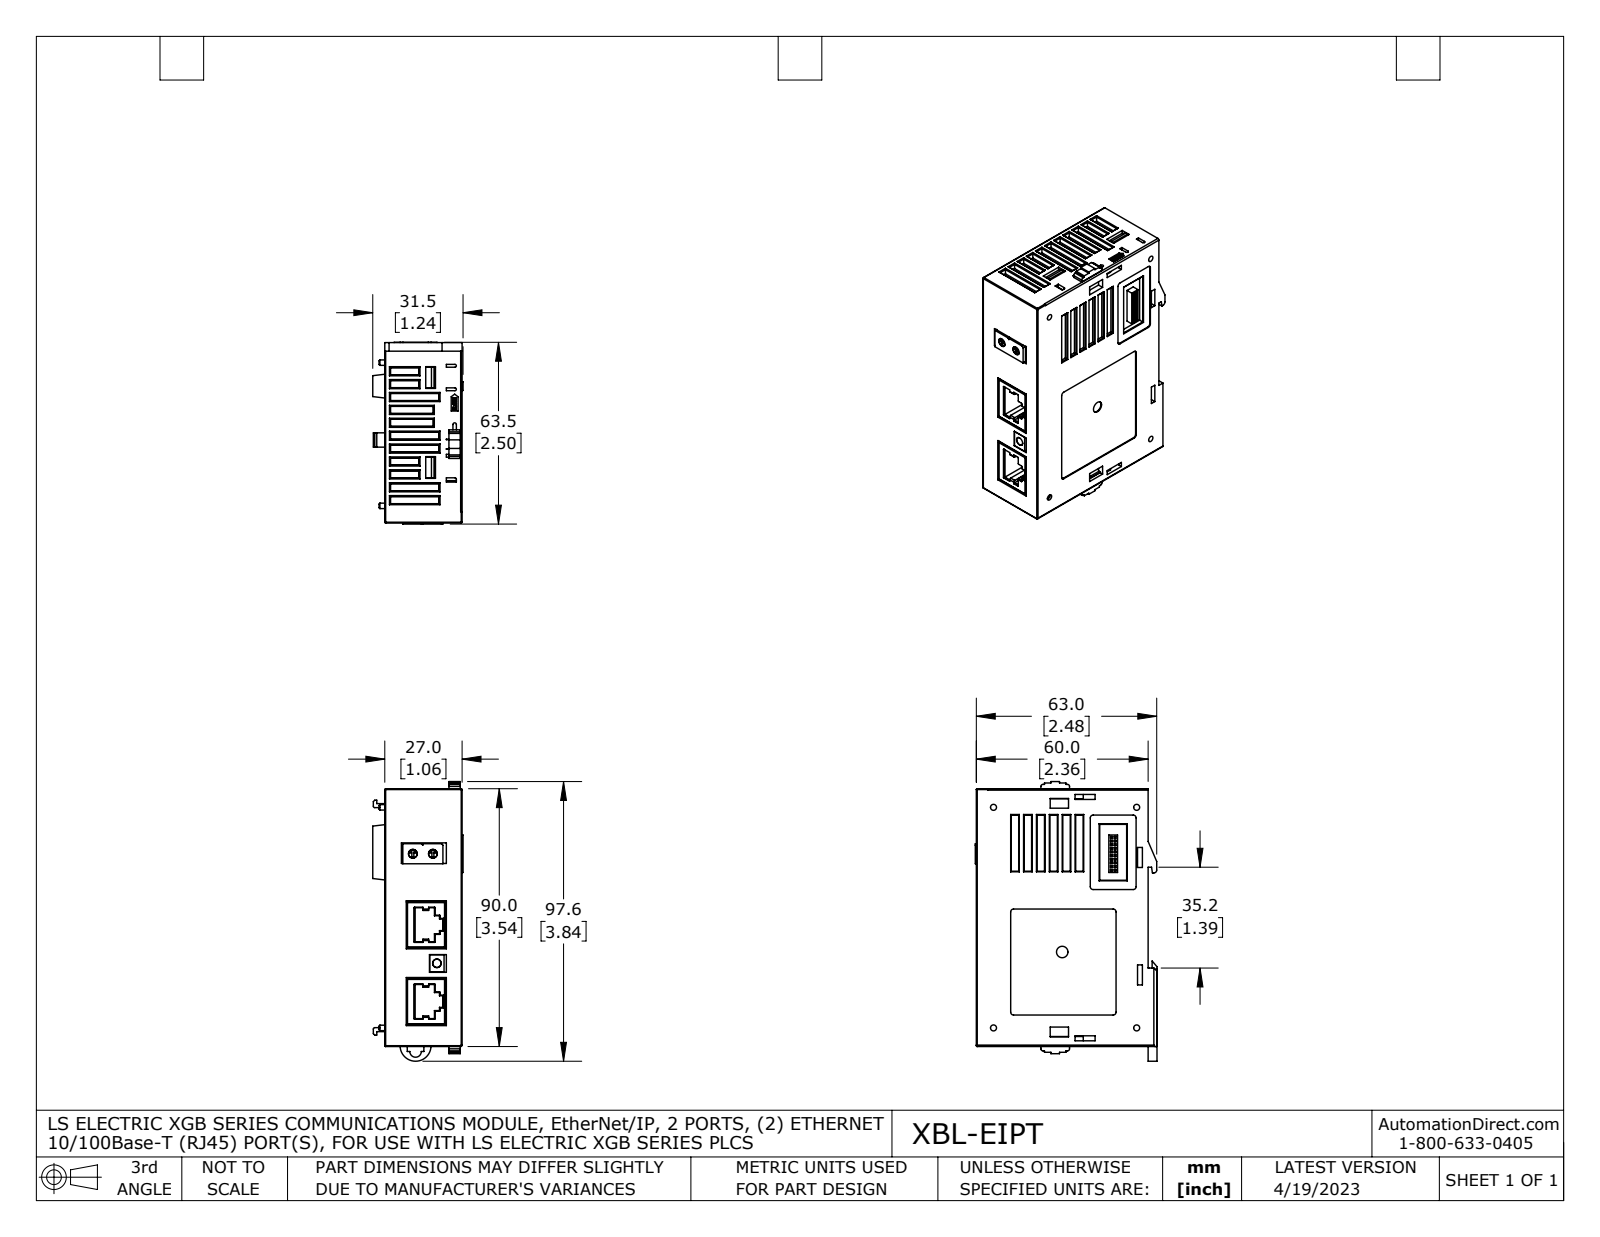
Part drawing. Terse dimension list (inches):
name: XBL-EIPT broken part cut1 coord fxt
written by: SolidWorks 2021 (AUTOMOTIVE_DESIGN)
unit: in
bodies: 2 solids, 2264 faces (1866 planar, 278 cylindrical, 120 other)
size: 3.844 × 2.498 × 1.241
volume: 7.993 in³; area: 54.84 in²
holes: 4× ⌀0.083, 2× ⌀0.071, 2× ⌀0.12, 1× ⌀0.118, 1× ⌀0.157
bosses: 4× ⌀0.075, 2× ⌀0.118, 2× ⌀0.071, 1× ⌀0.114
rounds: 40× R0.004, 23× R0.02, 22× R0.008, 16× R0.048, 15× R0.009, 12× R0.012, 10× R0.006, 9× R0.039
face distances: 0.079, 1.063, 0.039, 0.984, 2.362, 1.051, 1.024, 0.945, 0.067, 0.906
hole spacings: 0.539, 1.434, 1.969, 3.031, 3.135, 3.405, 3.615, 0.276
